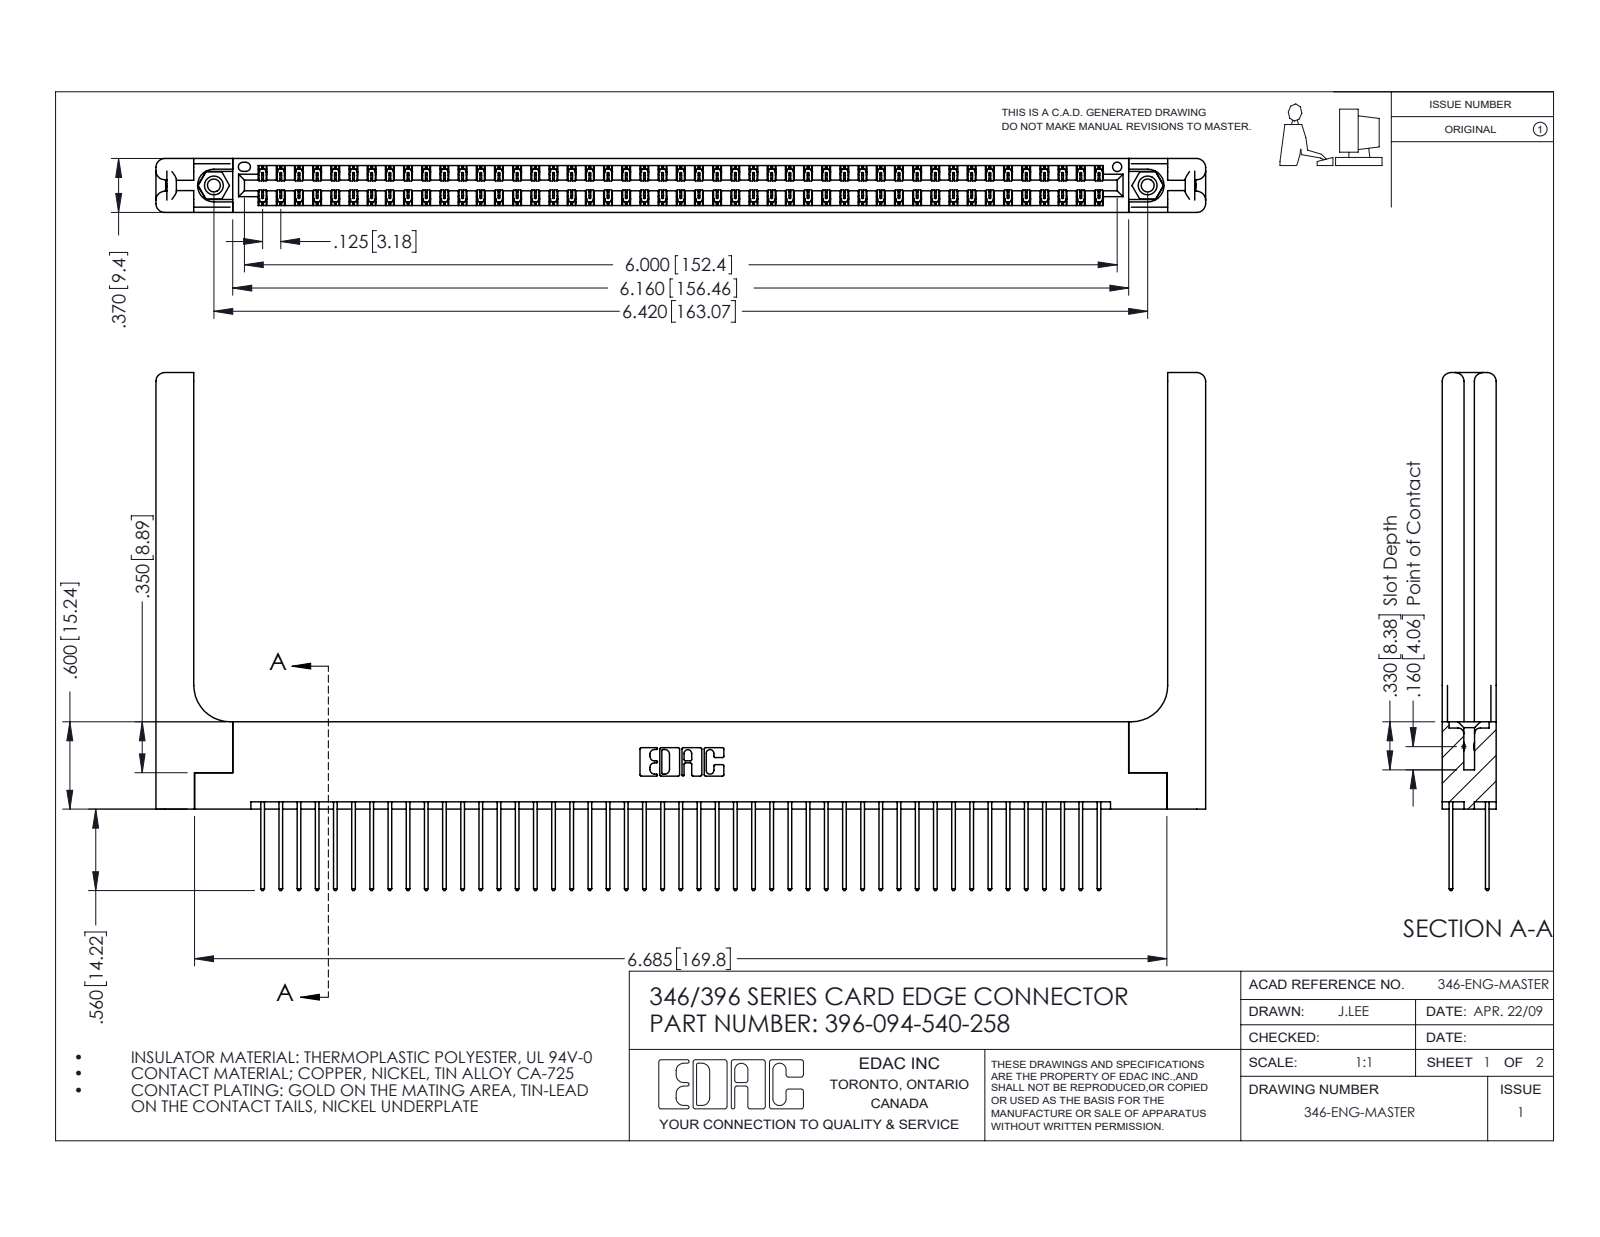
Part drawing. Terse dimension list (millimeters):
name: 346-220-058_345-220-058; 345-250-001_345-250-001-102; 346 Part_Flush Mounting Lugs - 0.156 Dia-TH; 396-094-540-258 (+1 more)
written by: SolidWorks 2016 (CONFIG_CONTROL_DESIGN)
unit: mm
bodies: 99 solids, 5266 faces (3514 planar, 1692 cylindrical, 60 other)
size: 183.3 × 90.4 × 9.4
volume: 25 760 mm³; area: 31 850 mm²
holes: 2× ⌀2.3, 2× ⌀3.2, 2× ⌀4, 1× ⌀1.6
bosses: 2× ⌀3.9
rounds: 141× R0.2, 94× R0.3, 22× R0.3, 16× R1.5, 6× R0.2, 6× R0.8, 3× R0.7, 2× R0.4
face distances: 1.2, 8.2, 1.8, 9.4, 6.4, 0.6, 7.6, 3.8, 3.8, 7
hole spacings: 6.2, 157.8, 163.1
